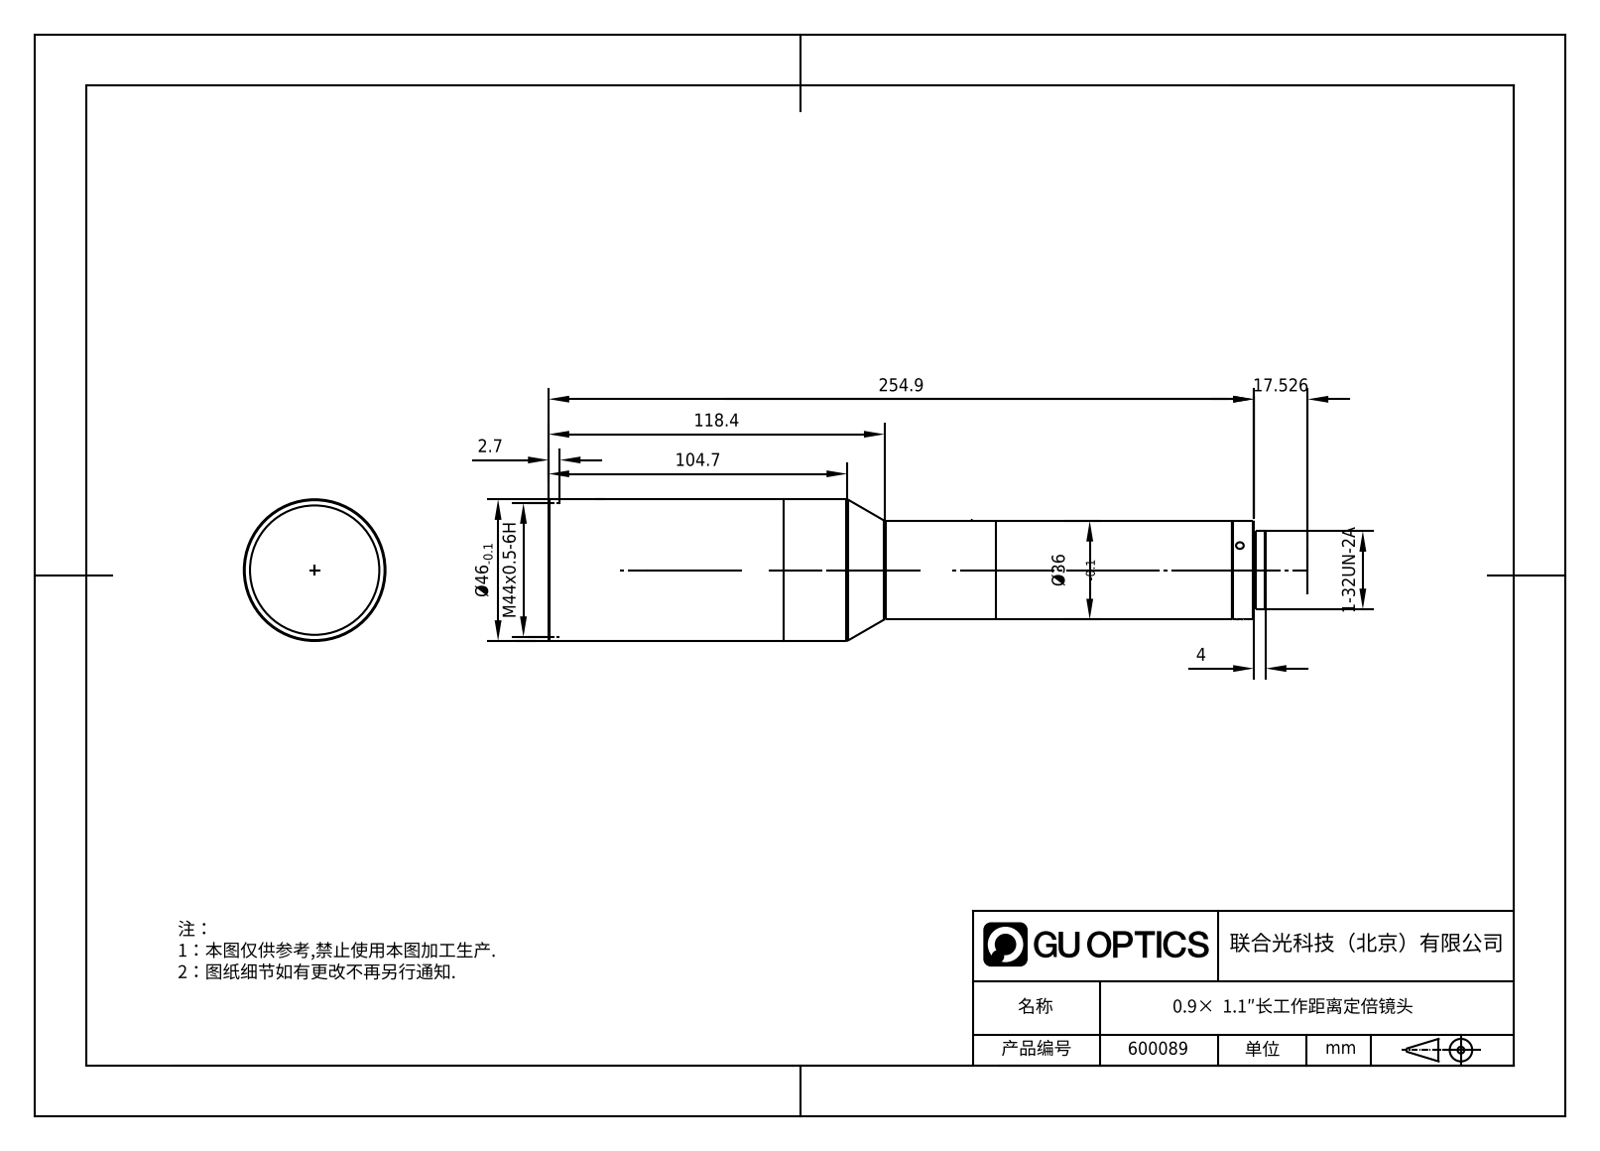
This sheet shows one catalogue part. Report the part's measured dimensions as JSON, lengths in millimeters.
{"part_name": "600089", "step_written_by": "SolidWorks 2020 (AUTOMOTIVE_DESIGN)", "units": "millimeters", "bodies": {"solids": 2, "faces": 34, "planar": 10, "cylindrical": 14, "other": 10}, "overall_size": [258.9, 46, 46], "volume_mm3": 327076, "surface_area_mm2": 40117, "round_holes": [[2.5, 3], [42, 1], [43.3, 1]], "round_bosses_or_shafts": [[46, 1], [43, 1], [36, 1], [25.4, 1], [24.6, 1]], "partial_cylinders_radius": [[17.18, 1]], "face_to_face_distances": [245.9, 4, 249.9, 258.9, 254.9, 9, 0.8, 170.03, 173.23, 169.23]}
